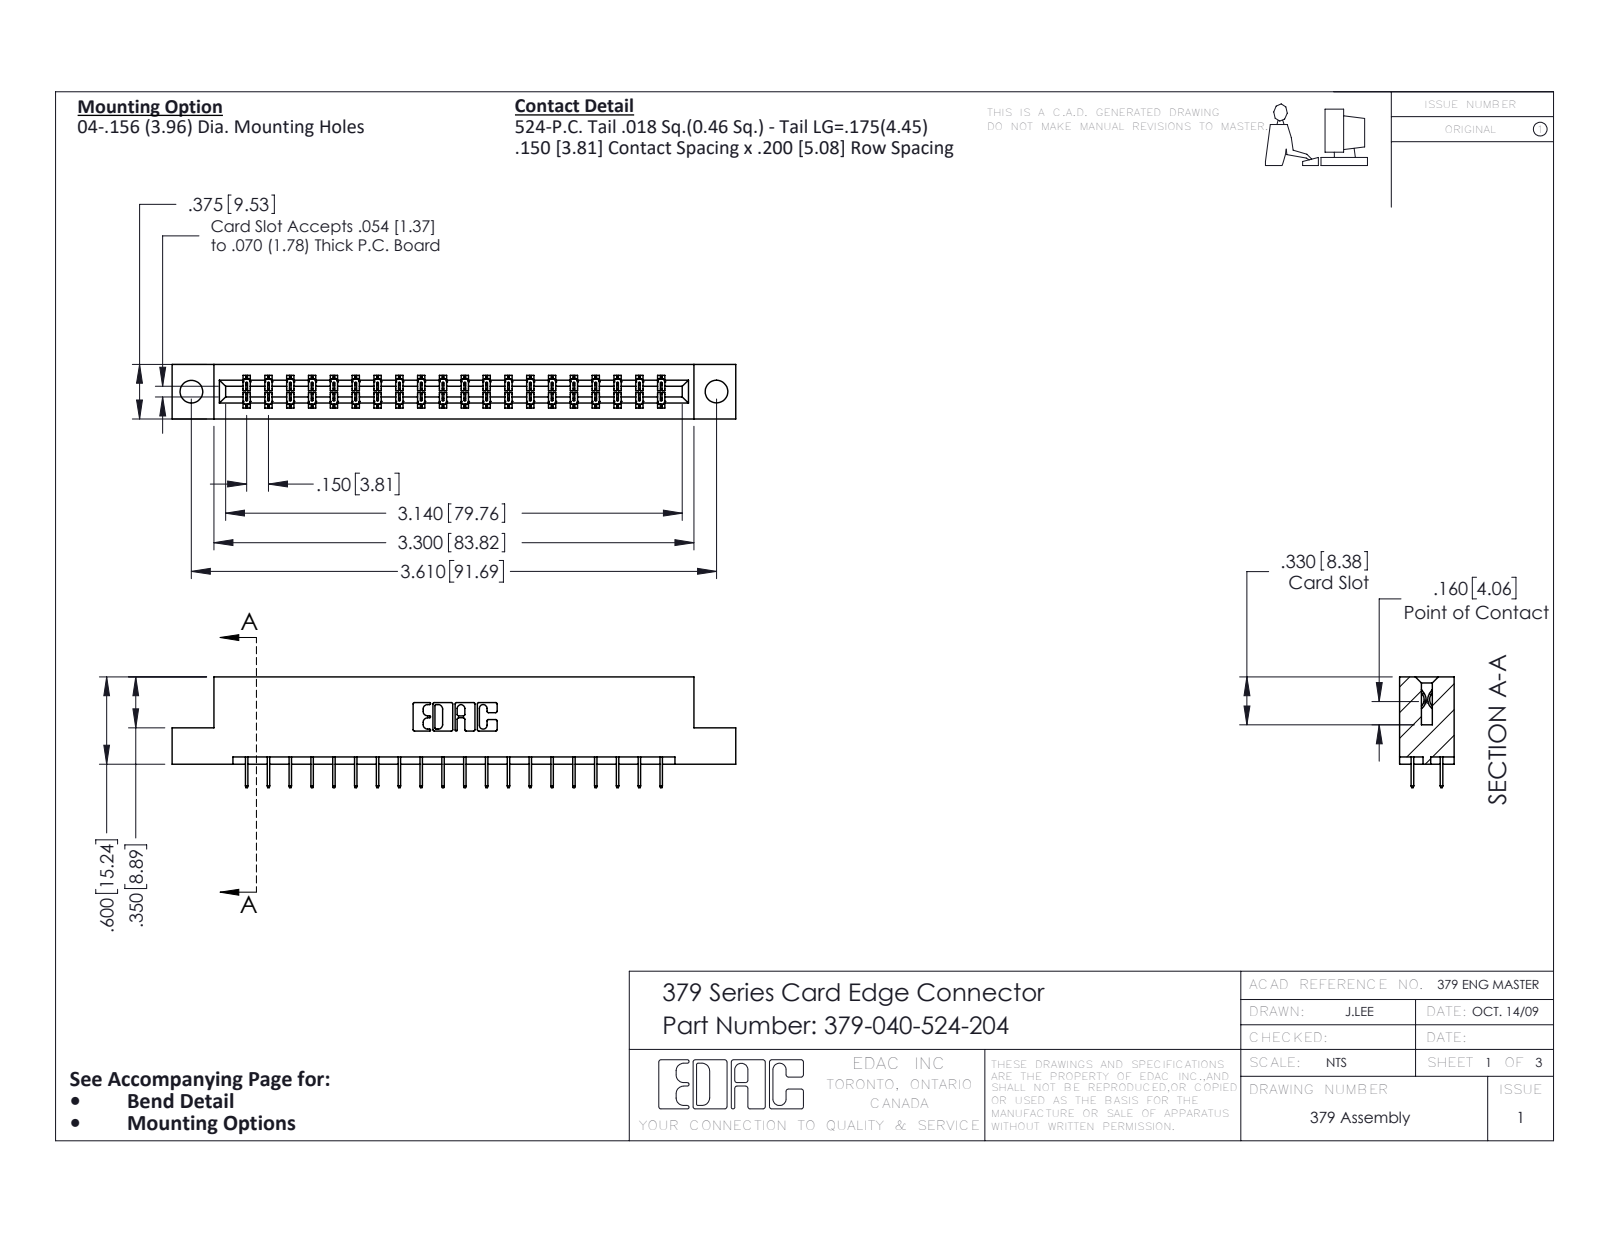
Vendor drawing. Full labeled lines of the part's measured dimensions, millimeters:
Part name (STEP PRODUCT): 345-292-001_345-293-124; 379 Part_Flush - .156 Dia - TH; 379-040-524-204
STEP written by: SolidWorks 2016 (CONFIG_CONTROL_DESIGN)
Units: millimetres
Bodies: 41 solids, 2354 faces (1750 planar, 604 cylindrical, 0 other)
Overall size (bounding box): 98.4 × 19.4 × 9.5
Volume: 10 100 mm³ · Surface area: 10 710 mm²
Round holes (diameter × count): ⌀4 ×2
Partial cylindrical surfaces — rounded edges, fillets, slot ends (radius × count): R0.2 ×60, R0.3 ×22, R0.2 ×6, R0.8 ×6, R0.7 ×3, R0.4 ×2, R0.6 ×2, R0.6 ×2
Main face-to-face distances: 7.6, 9.5, 1.9, 5.1, 2.5, 5.7, 3.8, 1.3, 15.2, 14
Hole centre spacings: 91.7
